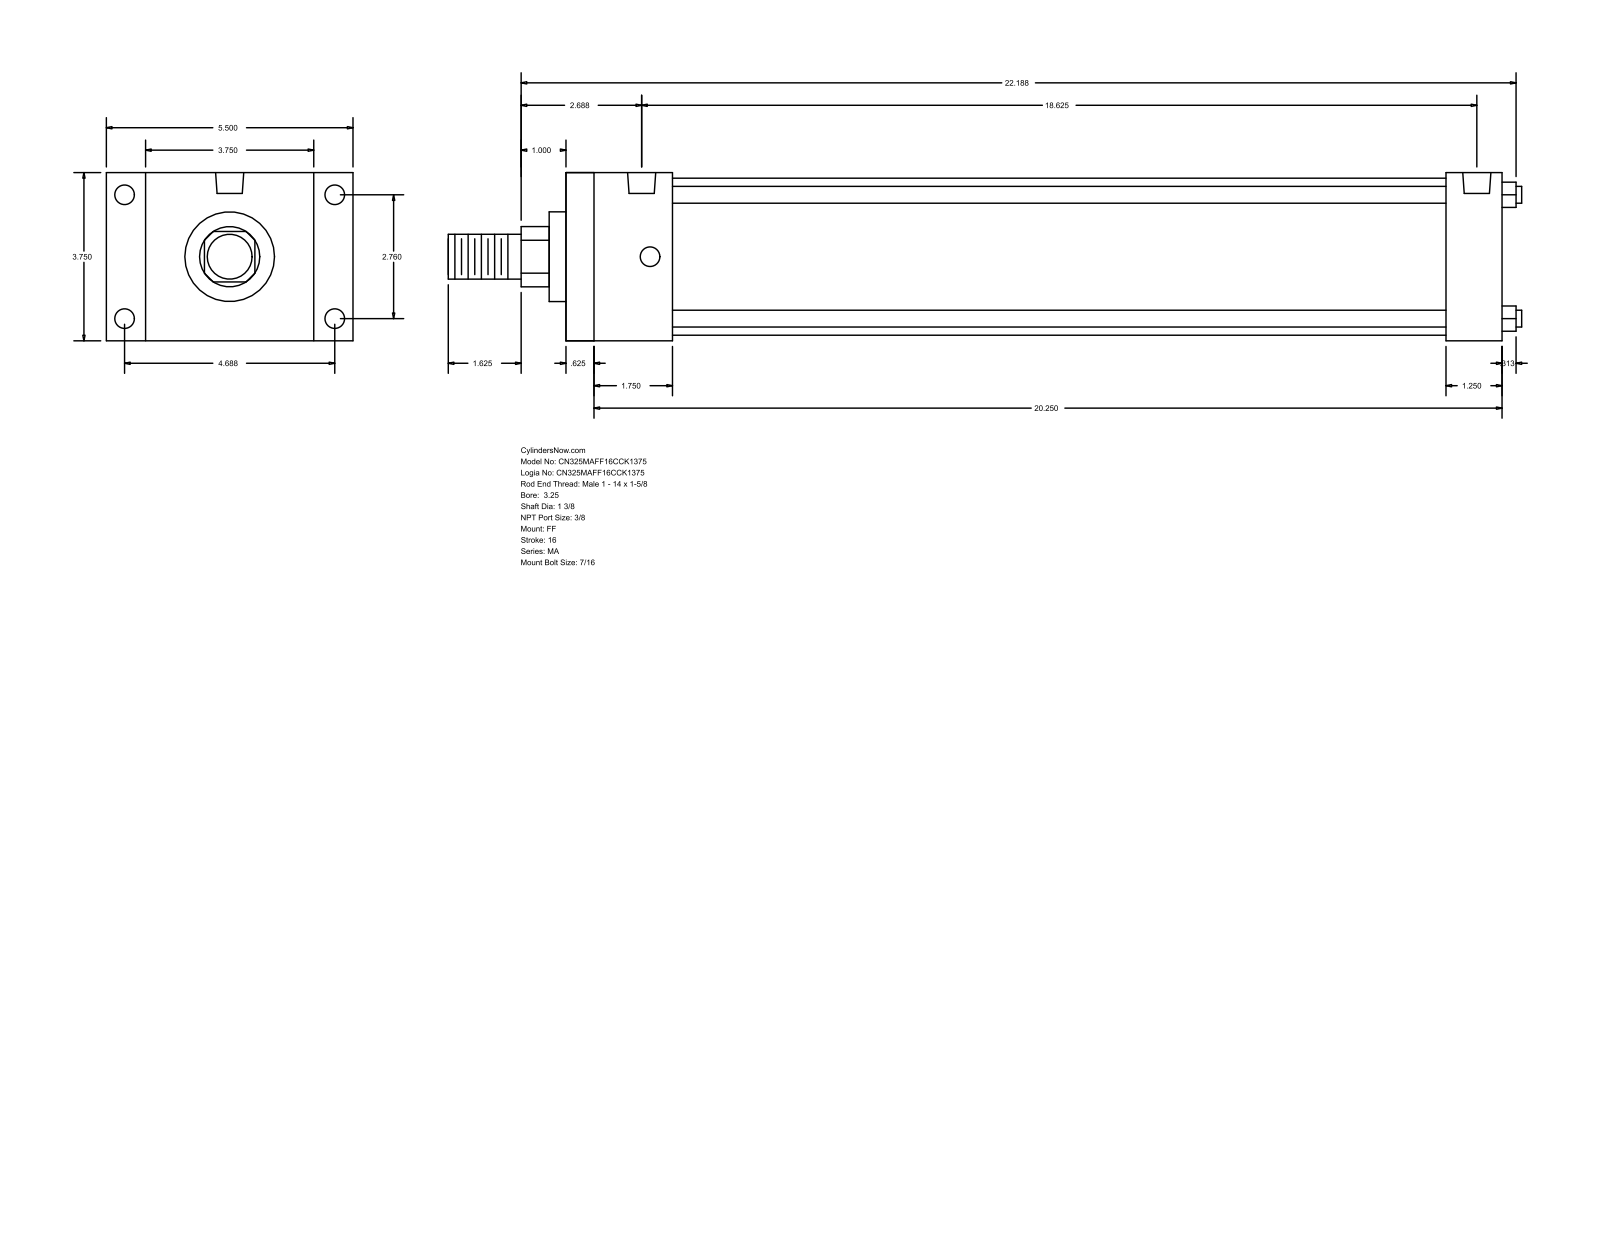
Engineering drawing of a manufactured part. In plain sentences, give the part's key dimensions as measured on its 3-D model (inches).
The part is named "MA_FF__0325_1.375". Its 3-D file was written by "GSSL Pune (CONFIG_CONTROL_DESIGN)". It is 0 solids with 92 faces: 64 planar, 28 cylindrical and 0 other. Overall it measures 23.937 by 5.5 by 3.75 inches. Round holes: 8 of diameter 0.437, 2 of diameter 0.627. Round bosses or shafts: 4 of diameter 0.375, 1 of diameter 3.5, 1 of diameter 2, 1 of diameter 1.375, 1 of diameter 1. Partial cylindrical surfaces (rounded edges, fillets, slot ends): 1 of radius 0.672. The main face-to-face distances are 3.75, 20.875, 0.625, 20.25, 0.875, 4.625, 2.375, 19.625, 1.75, 19. The hole center spacings are 2.76, 4.687, 5.439, 18.25, 0.187, 0.188, 18.437, 18.438.
